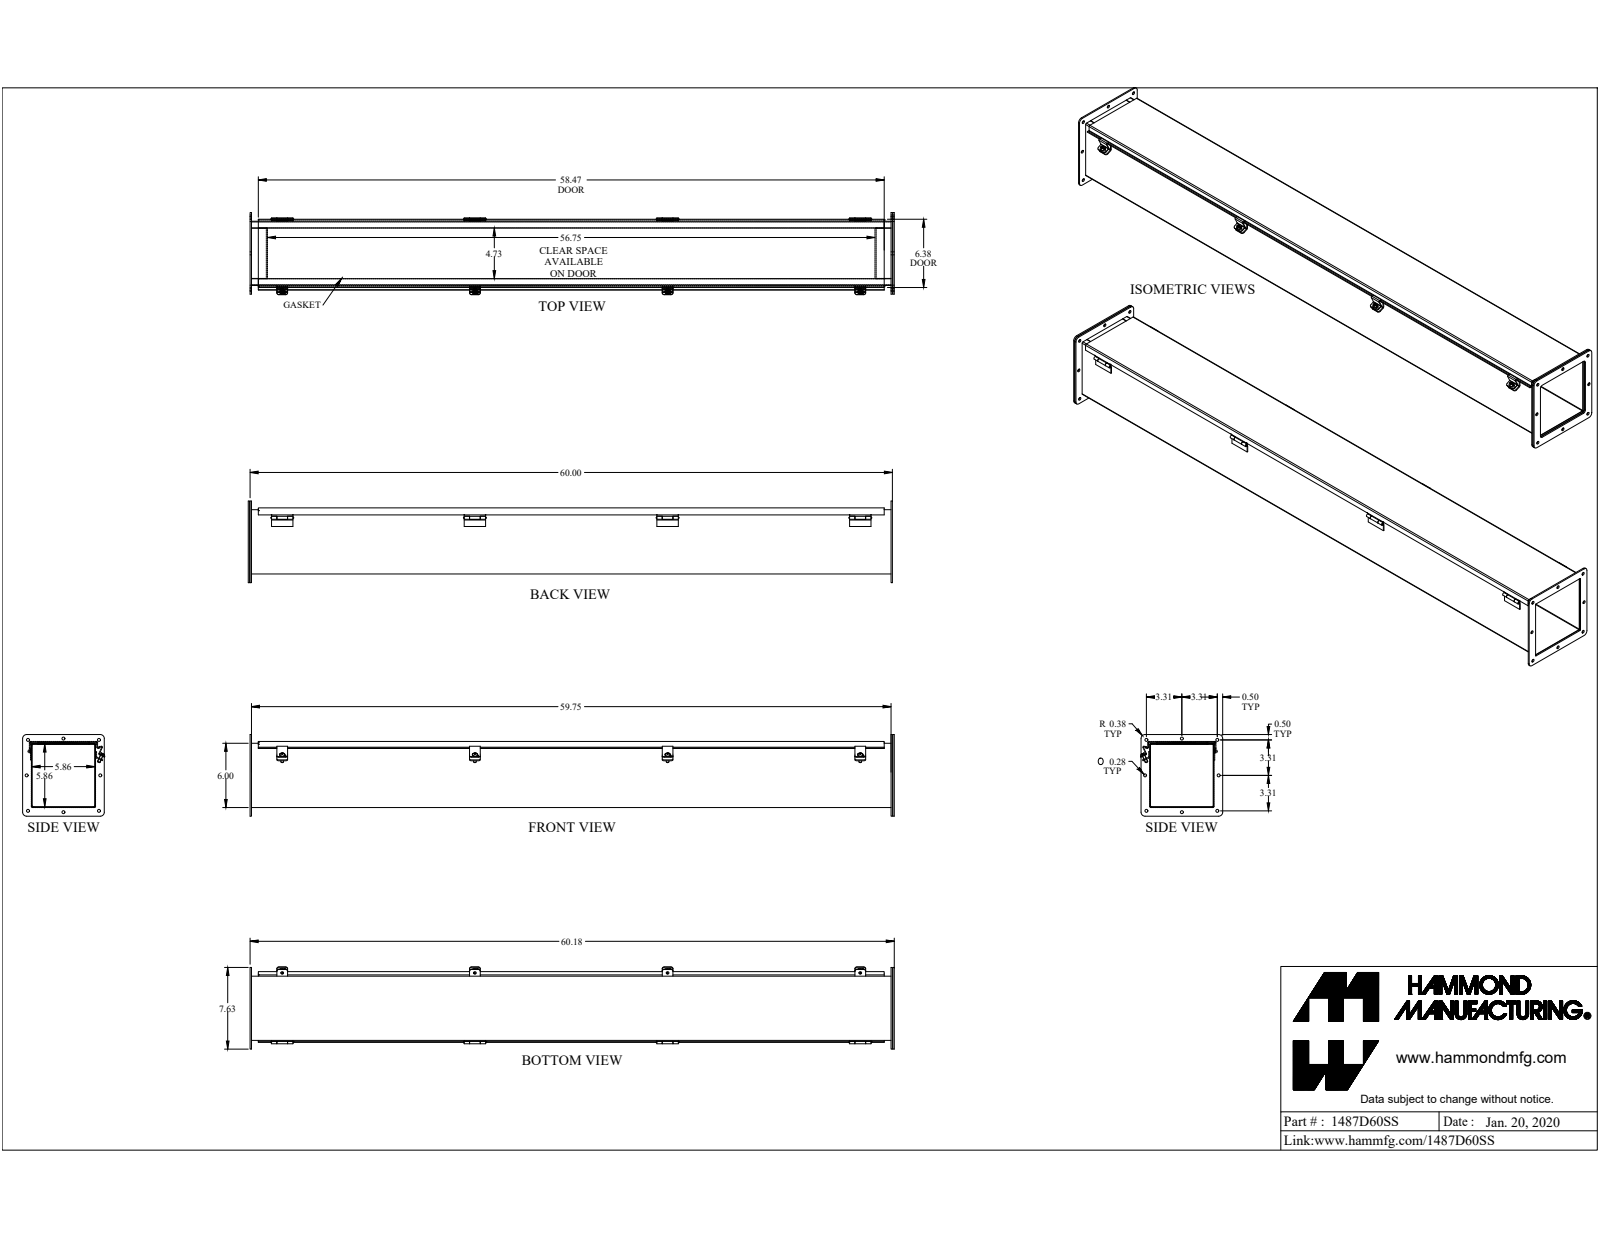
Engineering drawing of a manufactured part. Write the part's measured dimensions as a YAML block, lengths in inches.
part_name: "1487D60SS"
step_written_by: "SolidWorks 2019 (CONFIG_CONTROL_DESIGN)"
units: inches
bodies: {solids: 39, faces: 794, planar: 508, cylindrical: 216, other: 70}
overall_size: [60.546, 7.677, 7.625]
volume: 143.4
surface_area: 3690
round_holes:
  - {diameter: 0.281, count: 8}
  - {diameter: 0.213, count: 4}
  - {diameter: 0.187, count: 1}
  - {diameter: 0.196, count: 1}
  - {diameter: 0.258, count: 1}
  - {diameter: 0.35, count: 1}
round_bosses_or_shafts:
  - {diameter: 0.25, count: 5}
  - {diameter: 0.48, count: 4}
  - {diameter: 0.5, count: 1}
  - {diameter: 0.337, count: 1}
  - {diameter: 0.18, count: 1}
partial_cylinders:
  - {radius: 0.188, count: 16}
  - {radius: 0.03, count: 8}
  - {radius: 0.141, count: 8}
  - {radius: 0.375, count: 8}
  - {radius: 0.036, count: 7}
  - {radius: 0.108, count: 7}
  - {radius: 0.02, count: 6}
  - {radius: 0.063, count: 4}
face_to_face_distances: [0.072, 5.928, 6.1, 6, 5.856, 6.172, 6.028, 0.187, 0.259, 0.172]
hole_center_spacings: [7.519, 3.315, 18, 3.315, 4.861, 4.861, 6.625, 6.625]
